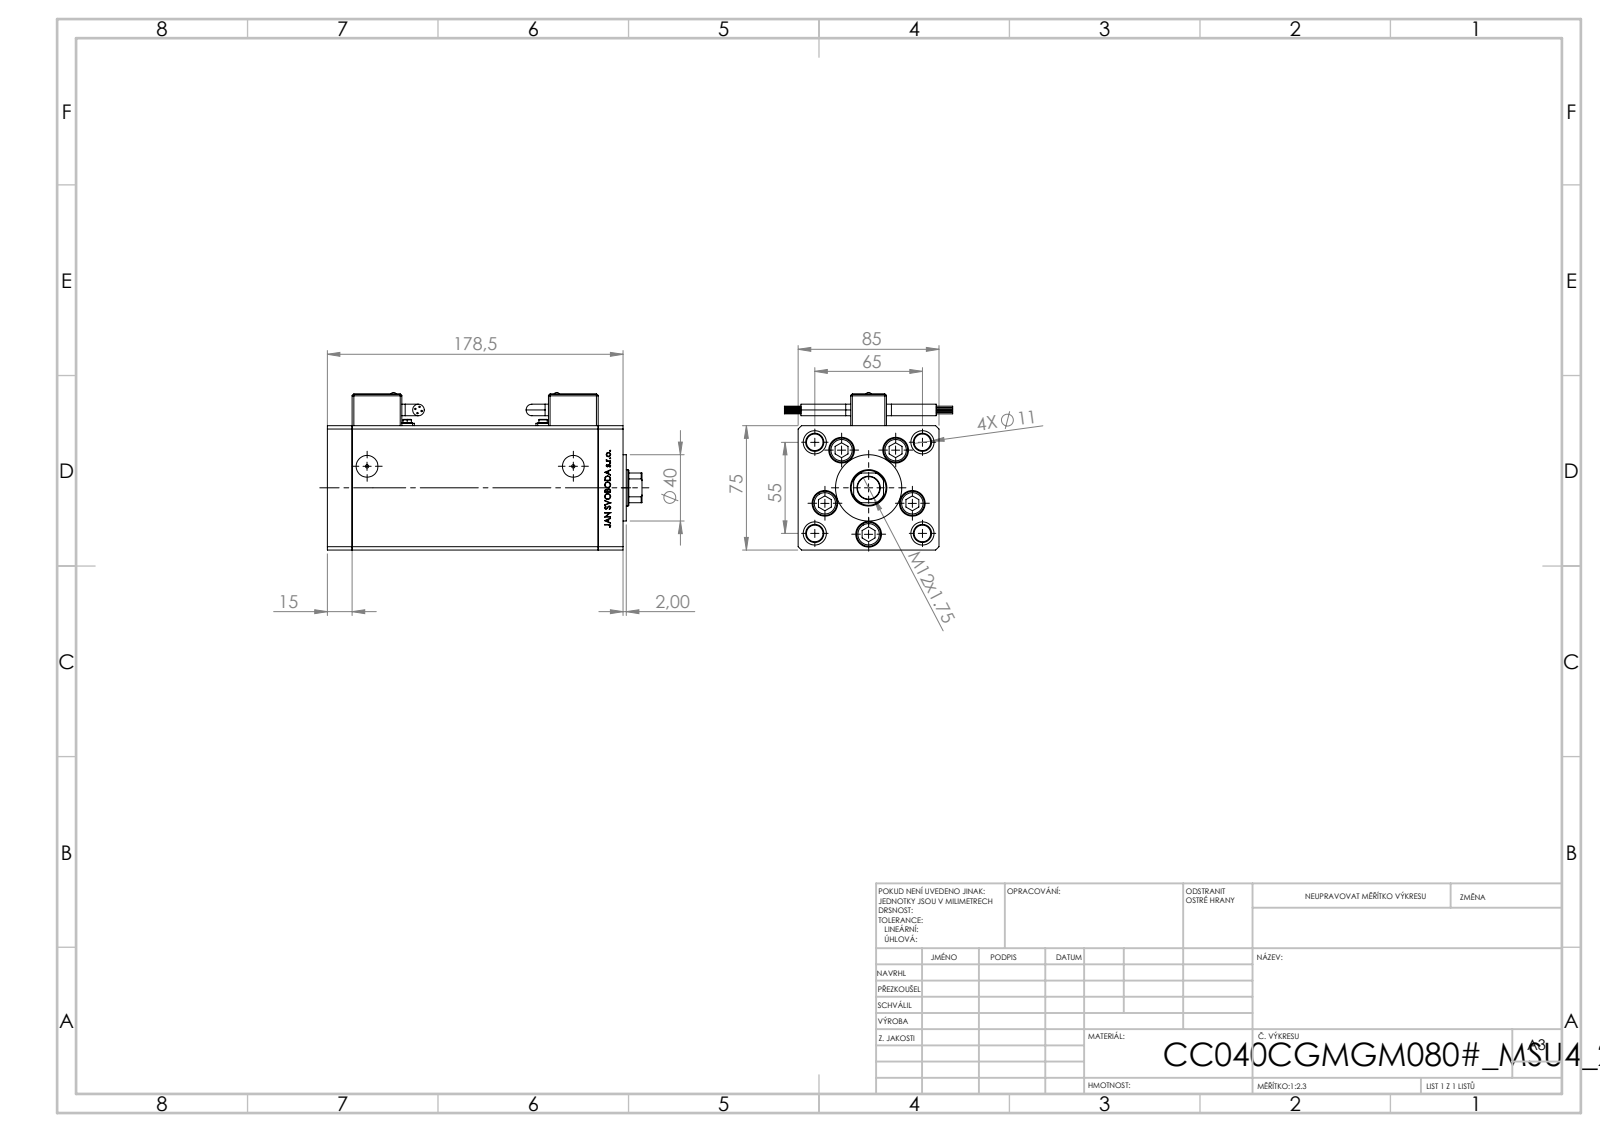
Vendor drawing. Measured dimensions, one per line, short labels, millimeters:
name: V220C_C MIDDLE; Magnetic_Switch_MSU4; ALLEN BOLT; V220C FRONT (+2 more)
written by: SolidWorks 2019 (CONFIG_CONTROL_DESIGN)
unit: mm
bodies: 15 solids, 1375 faces (620 planar, 257 cylindrical, 498 other)
size: 190 × 101.6 × 95.1
volume: 983 061 mm³; area: 191 820 mm²
holes: 9× ⌀11, 5× ⌀15.5, 4× ⌀10, 4× ⌀14, 2× ⌀2, 2× ⌀3.6, 2× ⌀5, 2× ⌀7, 2× ⌀13.16, 1× ⌀13.5, 1× ⌀14.5, 1× ⌀22
bosses: 8× ⌀0.85, 5× ⌀8, 4× ⌀14.5, 4× ⌀7, 2× ⌀6, 2× ⌀3.5, 2× ⌀2.5, 1× ⌀40
rounds: 24× R1, 4× R4, 2× R0.93, 1× R10.5
face distances: 85, 75, 15, 148.5, 163.5, 10.5, 68.5, 178.5, 34.25, 6.5
hole spacings: 28, 42.57, 8.25, 16.86, 19.17, 32.33, 32.5, 33.63
